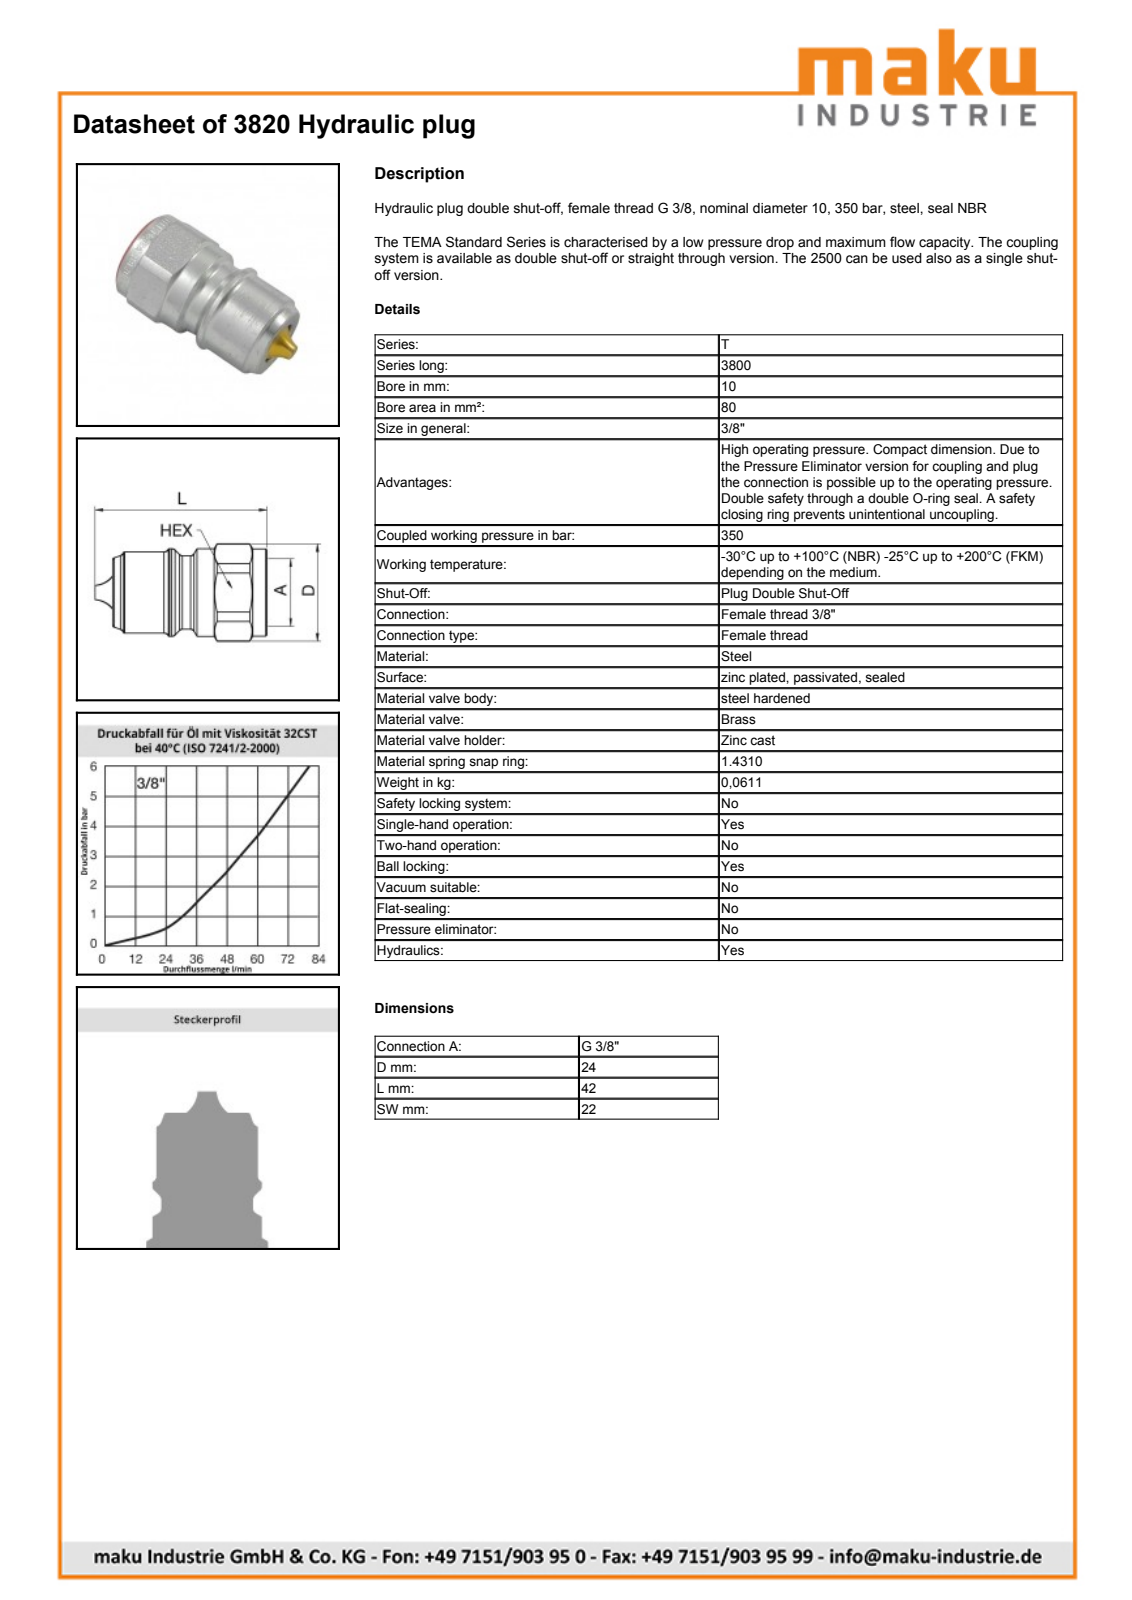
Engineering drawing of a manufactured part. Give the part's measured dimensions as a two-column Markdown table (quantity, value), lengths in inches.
| quantity | value |
| --- | --- |
| part name | 3820 |
| STEP written by | SolidWorks 2009 (AUTOMOTIVE_DESIGN) |
| units | inches |
| bodies | 1 solid, 58 faces (10 planar, 20 cylindrical, 28 other) |
| overall size | 1.668 × 0.945 × 0.866 |
| volume | 0.644 in³ |
| surface area | 6.295 in² |
| round holes (diameter × count) | 0.394 × 1, 0.589 × 1 |
| round bosses / shafts (diameter × count) | 0.858 × 1, 0.846 × 1, 0.799 × 1, 0.701 × 1 |
| partial cylindrical surfaces (radius × count) | 0.472 × 1 |
| main face-to-face distances | 0.866, 0.581, 0.915, 1.496, 0.172, 1.087, 1.668 |
